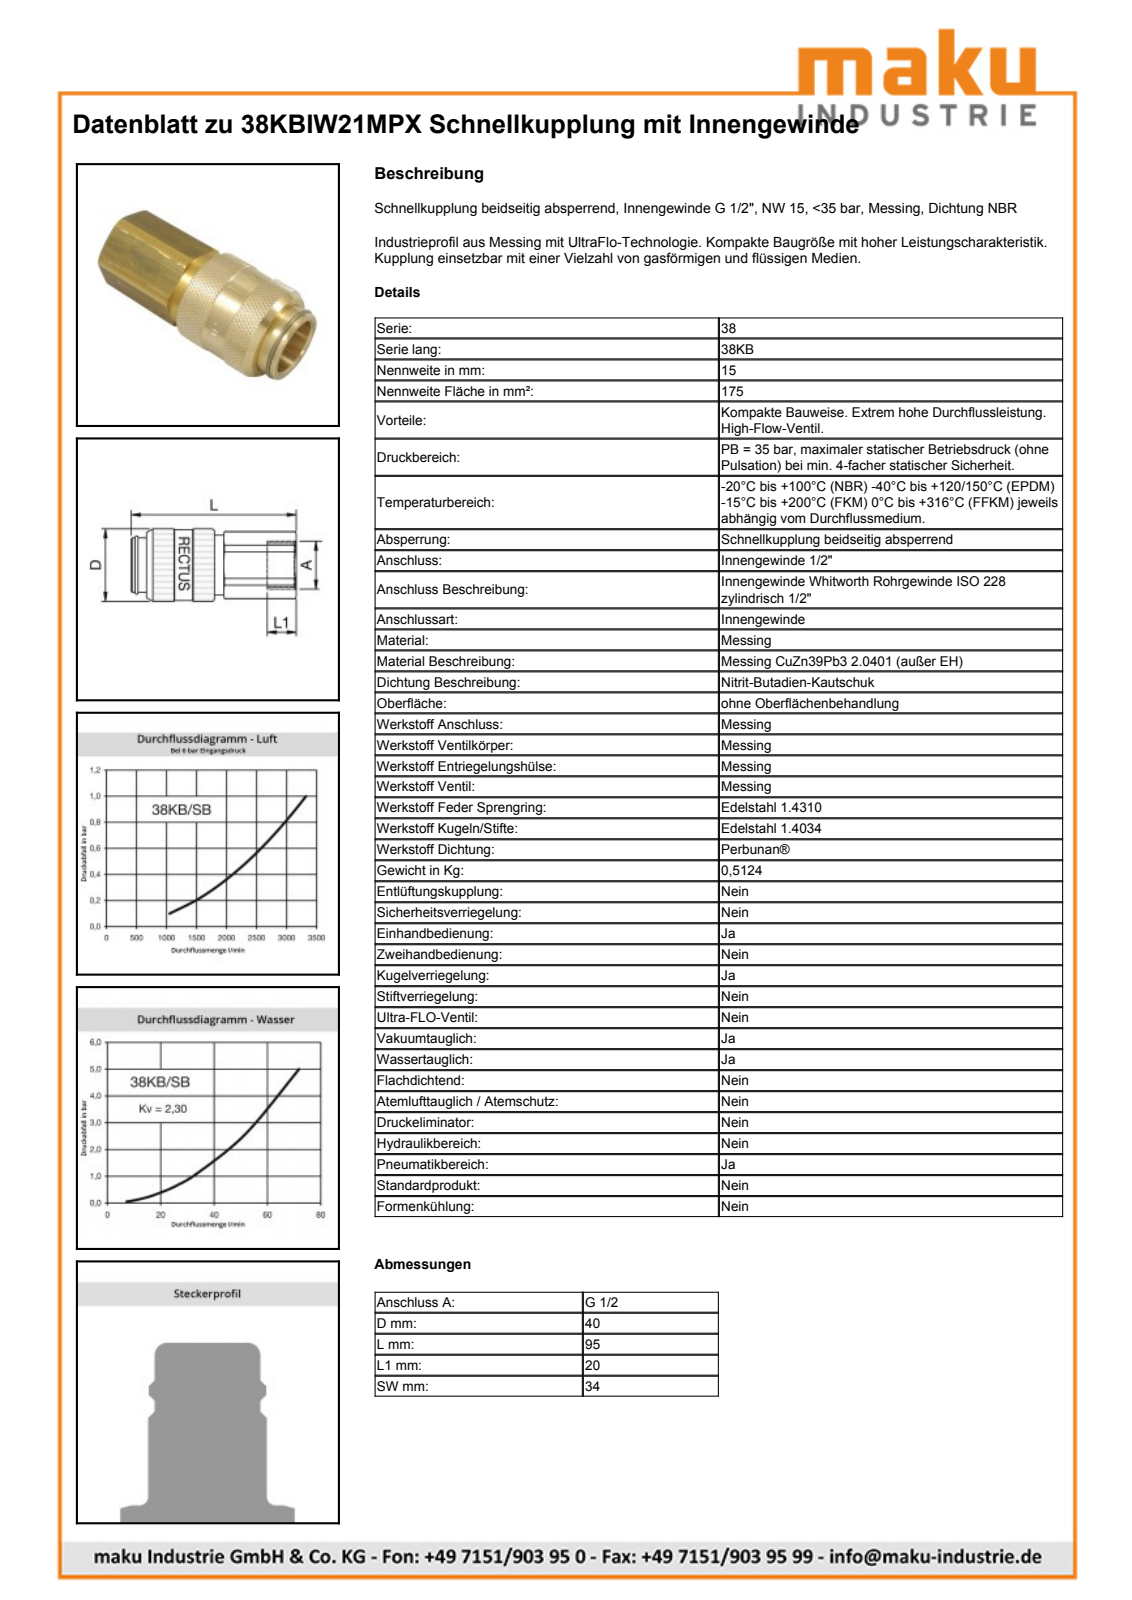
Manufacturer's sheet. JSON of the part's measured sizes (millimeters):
{"part_name": "D104483", "step_written_by": "Autodesk Inventor 2011 (AUTOMOTIVE_DESIGN)", "units": "millimeters", "bodies": {"solids": 2, "faces": 519, "planar": 185, "cylindrical": 75, "other": 259}, "overall_size": [91.05, 40, 40], "volume_mm3": 86585, "surface_area_mm2": 22782, "round_holes": [[18.63, 1], [30, 1], [30.75, 1], [34.45, 1], [34.6, 1]], "round_bosses_or_shafts": [[40, 1], [39, 1], [34, 1], [28.5, 1], [28.43, 1]], "partial_cylinders_radius": [[18.5, 1], [19.4, 1]], "face_to_face_distances": [34.02, 34, 91.05, 8.15, 82.9, 19.05, 72, 63.85, 29.65, 21.5]}
